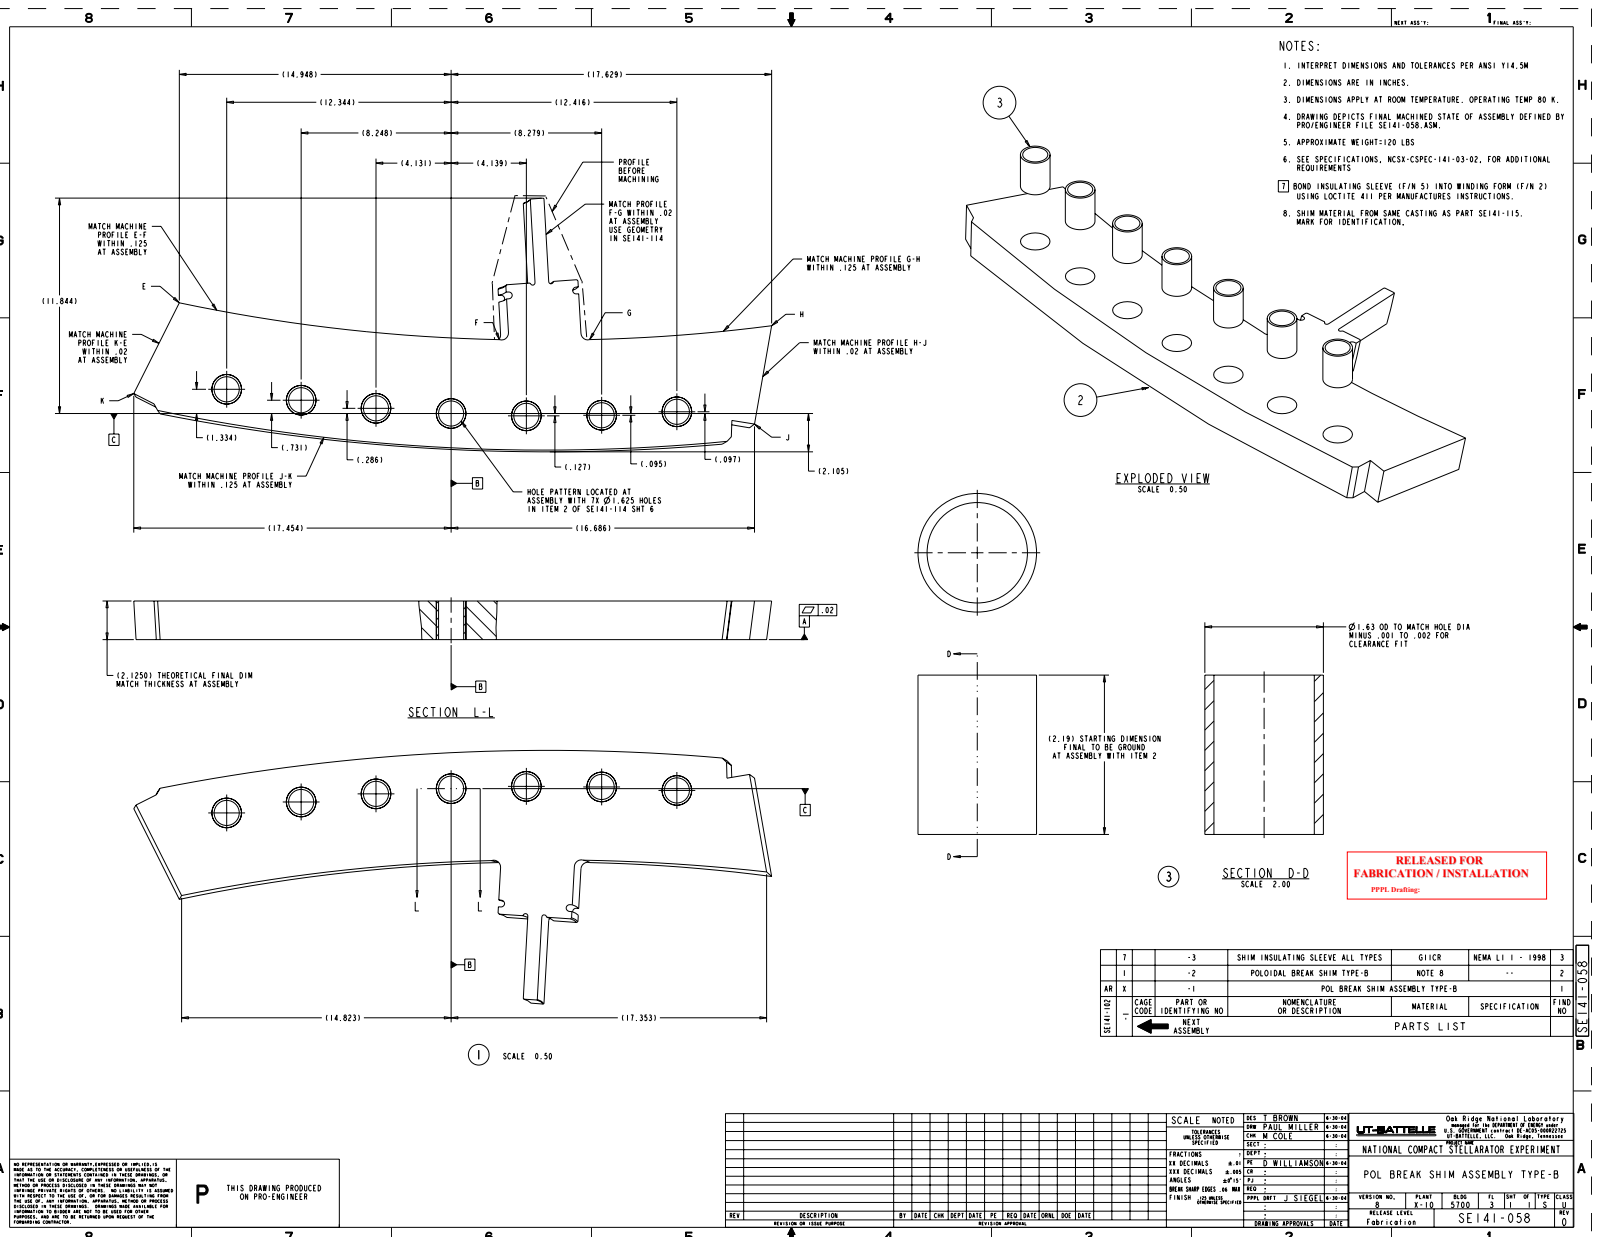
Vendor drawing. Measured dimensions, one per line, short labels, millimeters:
name: PEAR
written by: PRO/ENGINEER BY PARAMETRIC TECHNOLOGY CORPORATION, 2004440 (CONFIG_CONTROL_DESIGN)
unit: mm
bodies: 1 solid, 51 faces (2 planar, 14 cylindrical, 35 other)
size: 693 × 677.3 × 295.9
volume: 6 986 000 mm³; area: 438 700 mm²
holes: 7× ⌀41.3
face distances: 54
hole spacings: 210.3, 105.2, 315.4, 420.3, 105.2, 525.1, 525.1, 629.7
